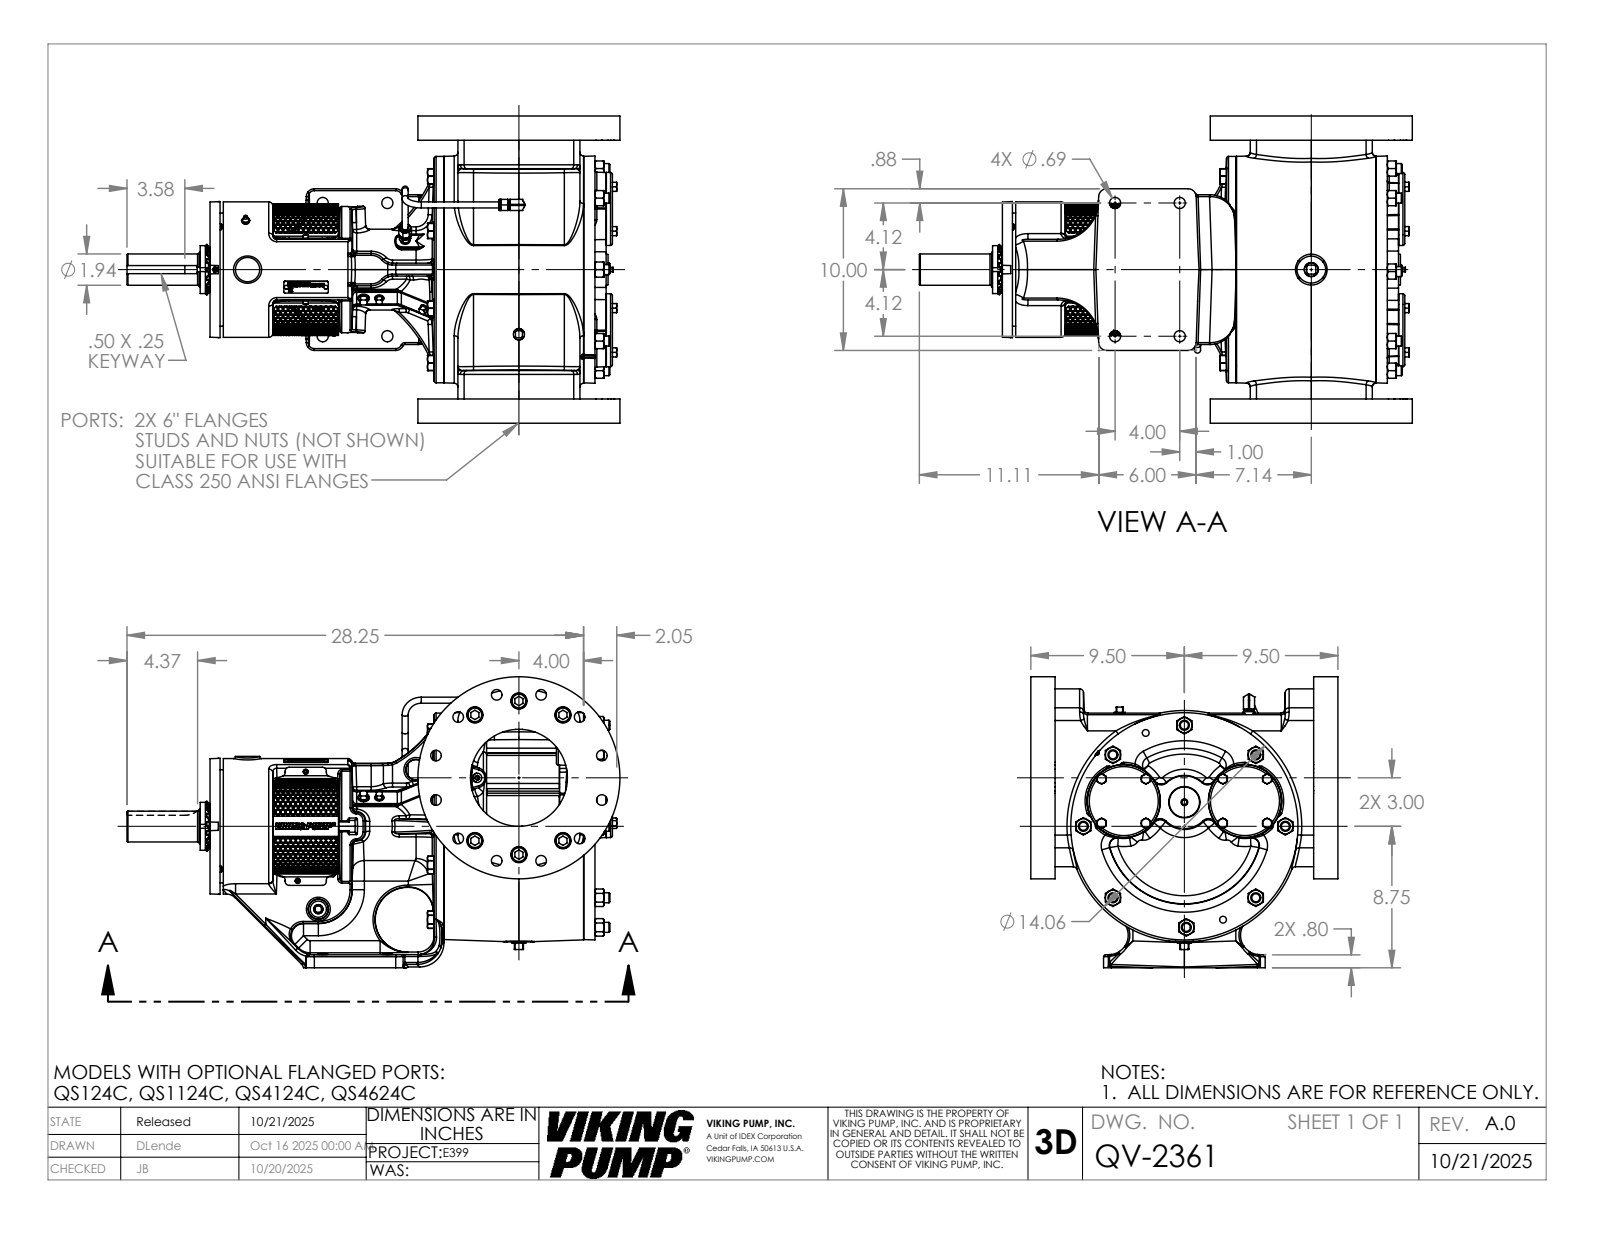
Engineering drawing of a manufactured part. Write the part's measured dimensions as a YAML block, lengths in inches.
part_name: "QV-2361"
step_written_by: "SolidWorks 2024 (AUTOMOTIVE_DESIGN)"
units: inches
bodies: {solids: 1, faces: 4177, planar: 1414, cylindrical: 684, other: 2079}
overall_size: [30.501, 19, 18]
volume: 2700
surface_area: 2567
round_holes:
  - {diameter: 0.656, count: 12}
  - {diameter: 0.25, count: 9}
  - {diameter: 0.266, count: 8}
  - {diameter: 1.157, count: 8}
  - {diameter: 1, count: 6}
  - {diameter: 0.688, count: 4}
  - {diameter: 0.159, count: 2}
  - {diameter: 0.313, count: 2}
  - {diameter: 0.422, count: 2}
  - {diameter: 0.453, count: 1}
  - {diameter: 2.157, count: 1}
  - {diameter: 2.167, count: 1}
round_bosses_or_shafts:
  - {diameter: 0.617, count: 8}
  - {diameter: 0.937, count: 6}
  - {diameter: 0.375, count: 5}
  - {diameter: 0.312, count: 3}
  - {diameter: 0.19, count: 3}
  - {diameter: 4.5, count: 2}
  - {diameter: 0.687, count: 2}
  - {diameter: 0.563, count: 2}
partial_cylinders:
  - {radius: 0.12, count: 60}
  - {radius: 0.25, count: 22}
  - {radius: 0.015, count: 18}
  - {radius: 0.092, count: 18}
  - {radius: 0.07, count: 16}
  - {radius: 0.75, count: 14}
  - {radius: 0.5, count: 13}
  - {radius: 1, count: 9}
face_to_face_distances: [1.5, 17.5, 19, 16, 0.57, 23.817, 3.82, 19.998, 22.268, 24.898]
hole_center_spacings: [5.313, 3.75, 2.079, 10.263, 5.783, 2.713, 2.75, 3.133]
